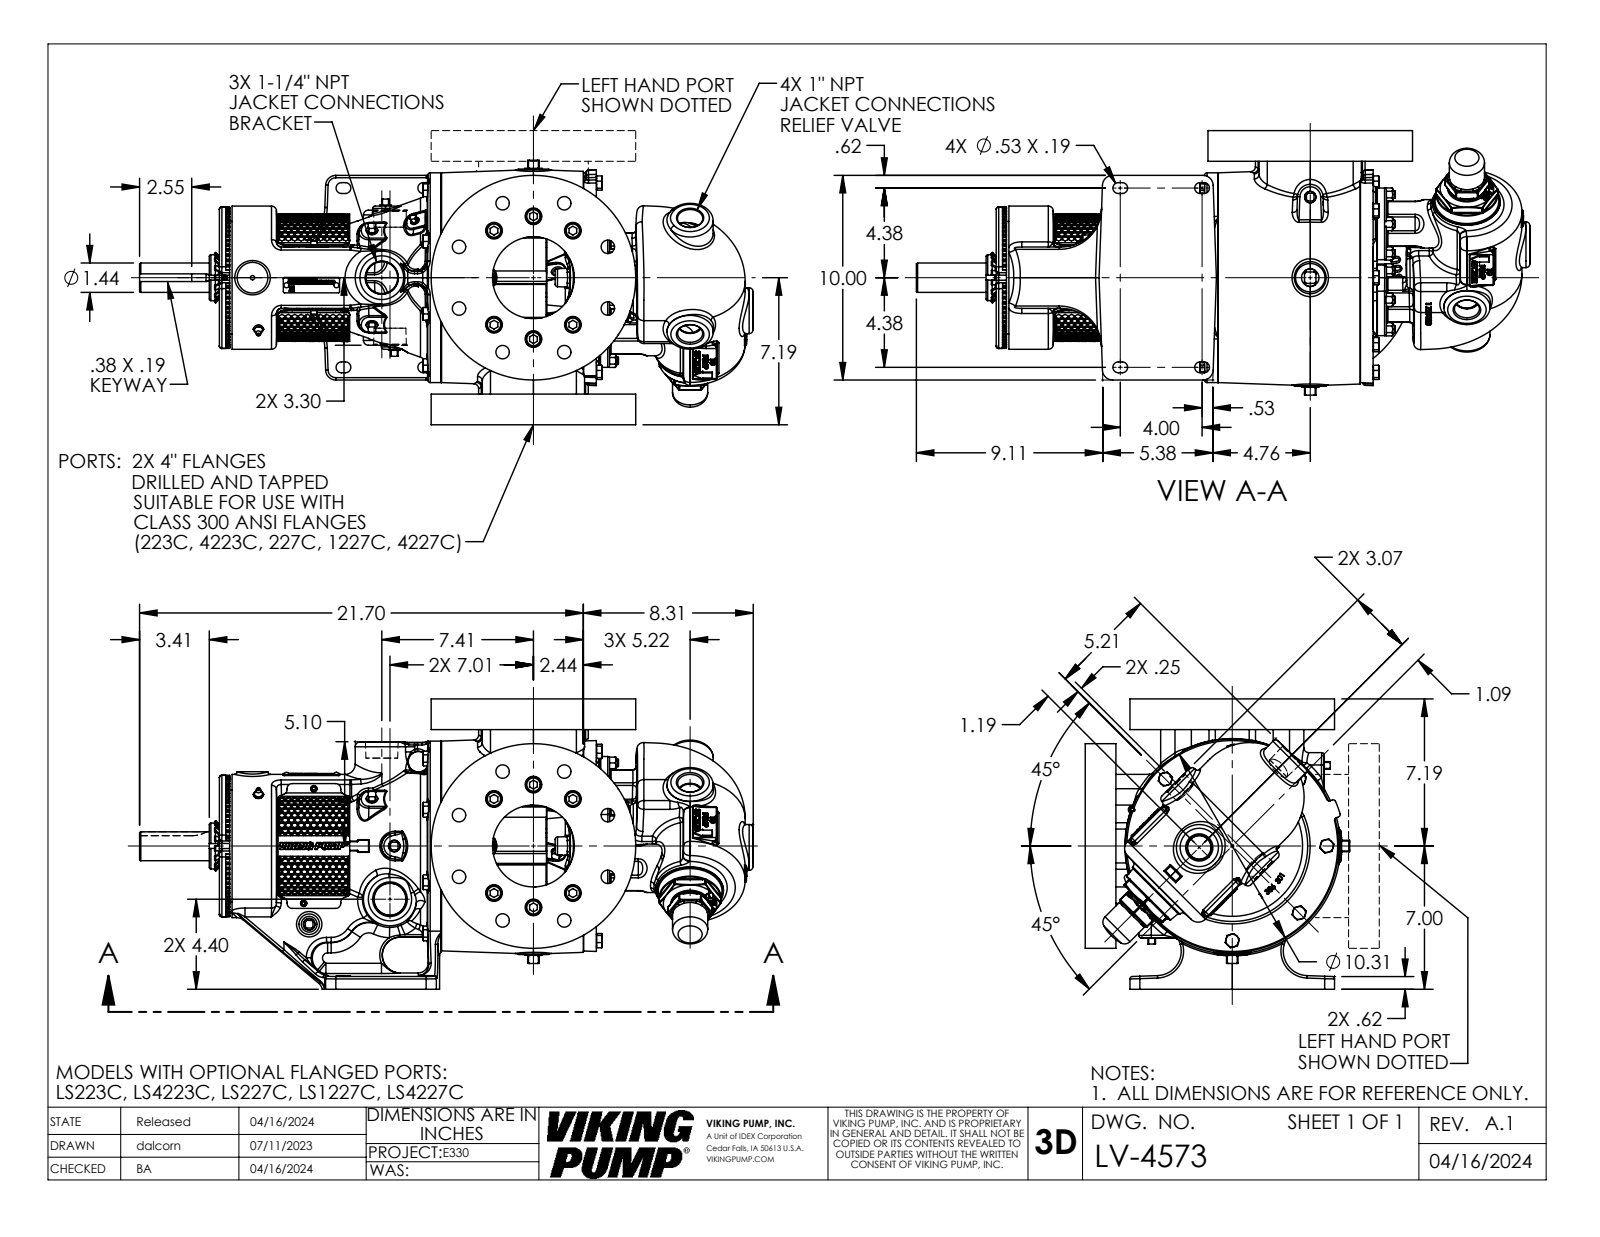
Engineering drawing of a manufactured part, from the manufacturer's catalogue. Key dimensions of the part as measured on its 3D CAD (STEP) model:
Part name (STEP PRODUCT): LV-4573
STEP written by: SolidWorks 2024 (AUTOMOTIVE_DESIGN)
Units: inches
Bodies: 1 solid, 5719 faces (1880 planar, 1021 cylindrical, 2818 other)
Overall size (bounding box): 29.994 × 14.188 × 12.863
Volume: 1 495 in³ · Surface area: 1 888 in²
Round holes (diameter × count): ⌀0.656 ×16, ⌀0.563 ×12, ⌀0.812 ×12, ⌀1.094 ×8, ⌀0.199 ×6, ⌀0.25 ×6, ⌀0.159 ×3, ⌀0.266 ×2, ⌀0.313 ×2, ⌀0.375 ×2, ⌀4 ×2, ⌀0.453 ×1
Round bosses / shafts (diameter × count): ⌀0.75 ×12, ⌀0.5 ×12, ⌀0.625 ×10, ⌀0.369 ×8, ⌀0.625 ×6, ⌀3.5 ×3, ⌀0.437 ×3, ⌀0.312 ×3
Partial cylindrical surfaces — rounded edges, fillets, slot ends (radius × count): R0.063 ×109, R0.12 ×84, R0.069 ×74, R0.03 ×36, R0.5 ×36, R0.24 ×16, R1 ×16, R0.19 ×14
Main face-to-face distances: 1.5, 12.687, 14.187, 0.5, 2.25, 15.669, 3.541, 12.128, 2.75, 2.139
Hole centre spacings: 3, 3.937, 5.569, 7.276, 1.375, 1.405, 1.636, 1.884
